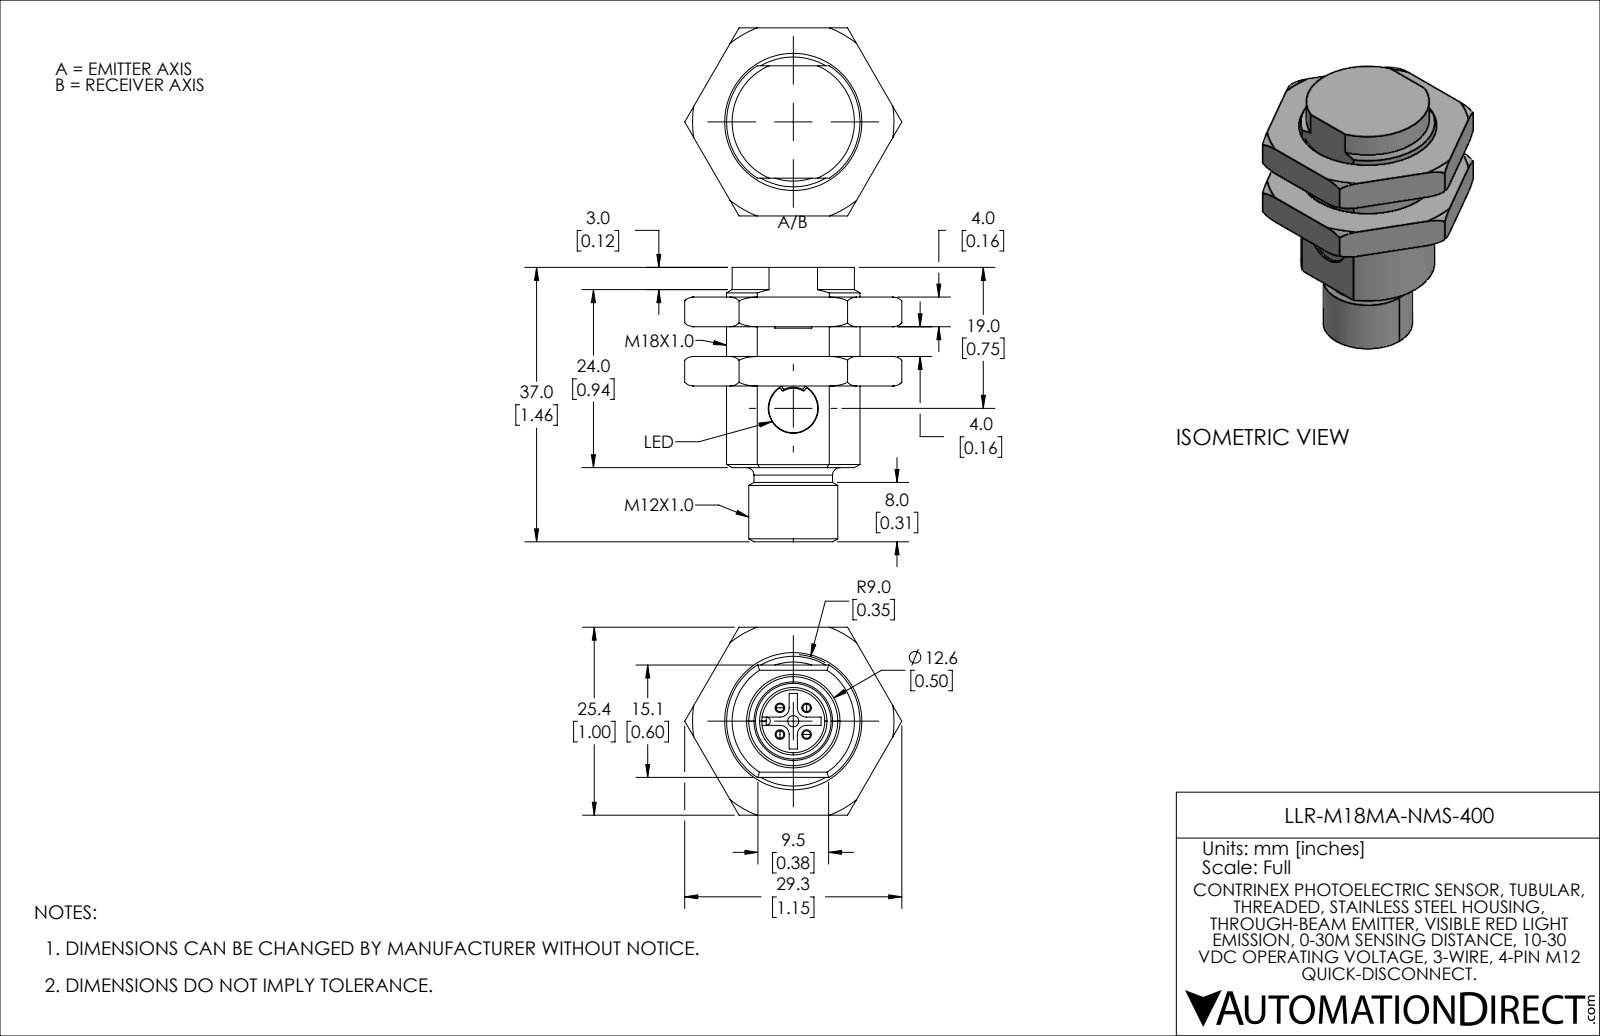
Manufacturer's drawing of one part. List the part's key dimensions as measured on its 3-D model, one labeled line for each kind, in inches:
Part name (STEP PRODUCT): LLR-M18MA-NMS-400
STEP written by: SolidWorks 2021 (AUTOMOTIVE_DESIGN)
Units: inches
Bodies: 3 solids, 176 faces (65 planar, 50 cylindrical, 61 other)
Overall size (bounding box): 1.457 × 1.153 × 0.998
Volume: 0.572 in³ · Surface area: 7.737 in²
Round holes (diameter × count): ⌀0.059 ×1, ⌀0.266 ×1, ⌀0.335 ×1, ⌀0.689 ×1
Round bosses / shafts (diameter × count): ⌀0.039 ×4, ⌀0.472 ×1, ⌀0.417 ×1
Partial cylindrical surfaces — rounded edges, fillets, slot ends (radius × count): R0.004 ×4, R0.006 ×4, R0.049 ×4, R0.02 ×2, R0.022 ×1, R0.106 ×1, R0.112 ×1, R0.325 ×1
Main face-to-face distances: 0.157, 0.315, 0.472, 0.998, 0.201, 0.798, 0.597, 0.63, 0.433, 0.591
